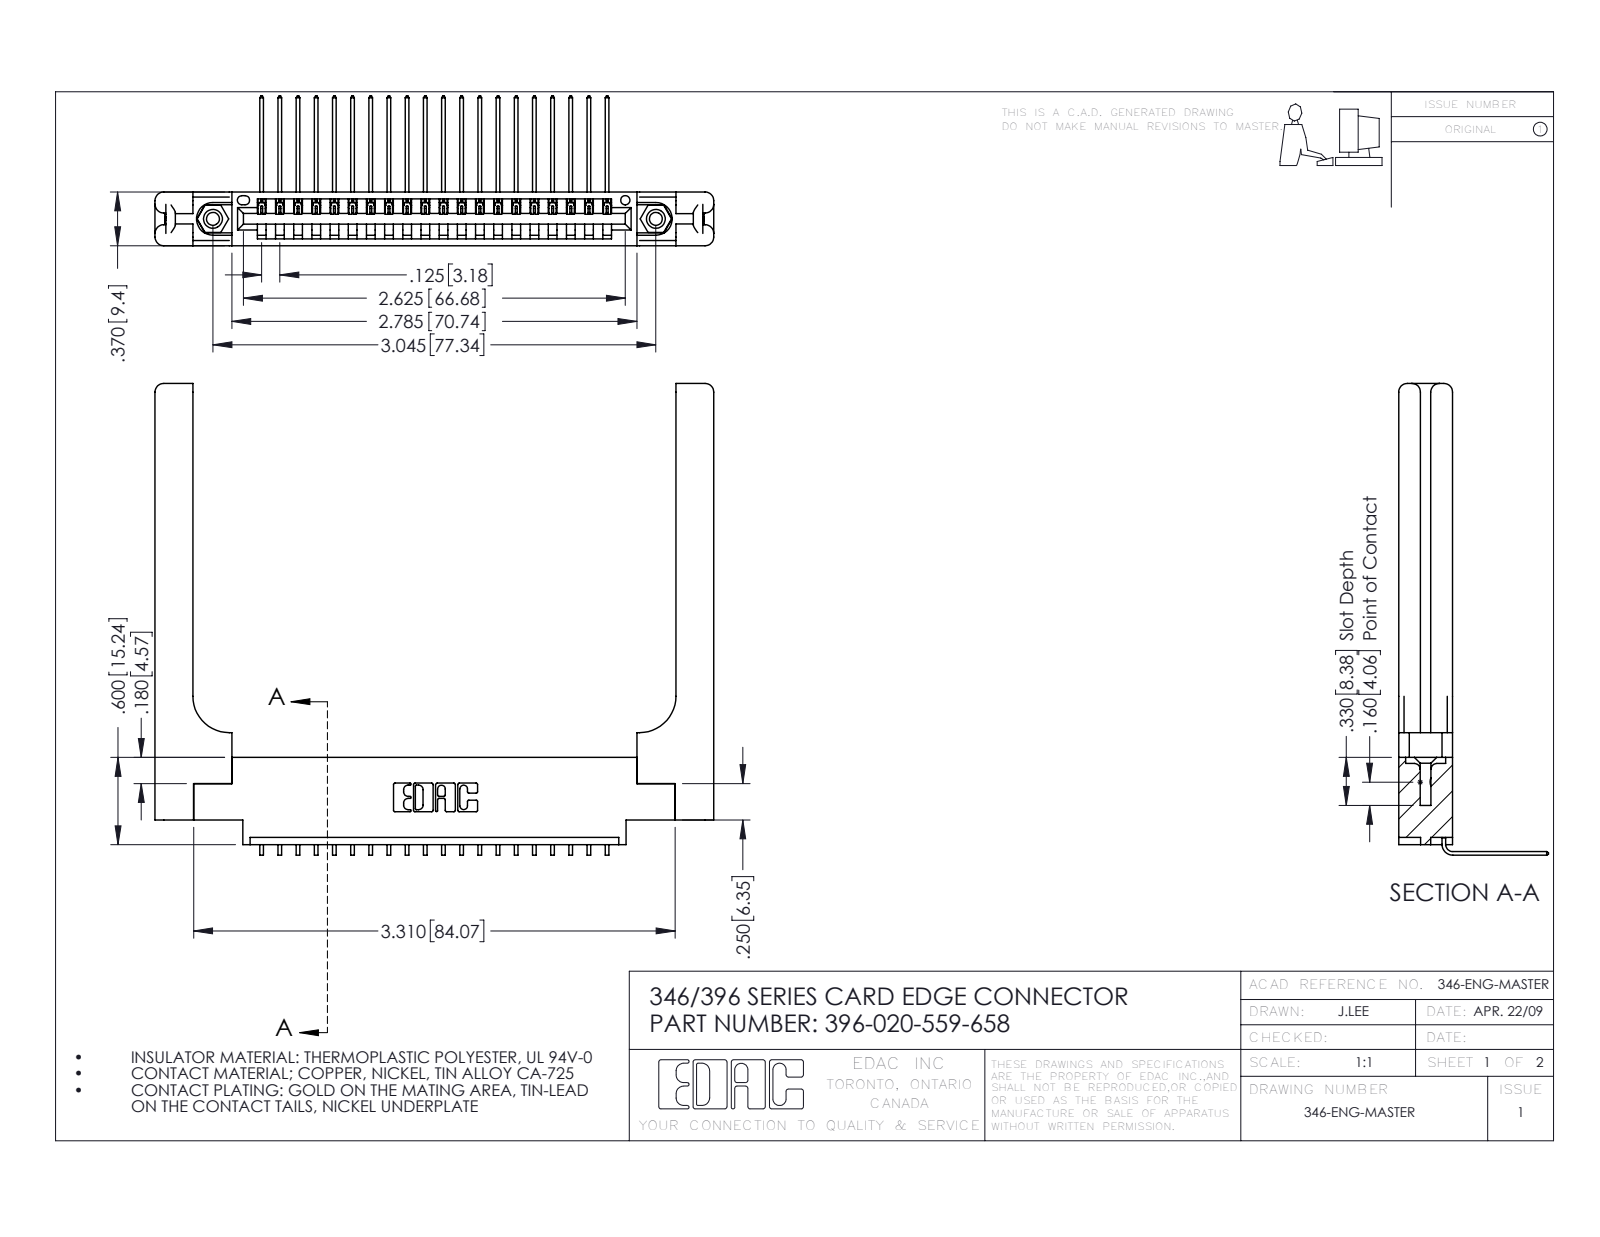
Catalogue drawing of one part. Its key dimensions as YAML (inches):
part_name: "346 Part_0.170 Offset - 0.156 Dia-TH; 396-020-559-658; 345-292-001_558 559 Tail - 1; 346-220-058_345-220-058 (+1 more)"
step_written_by: "SolidWorks 2016 (CONFIG_CONTROL_DESIGN)"
units: inches
bodies: {solids: 25, faces: 1582, planar: 1068, cylindrical: 454, other: 60}
overall_size: [3.841, 3.243, 1.03]
volume: 1.014
surface_area: 26.14
round_holes:
  - {diameter: 0.089, count: 2}
  - {diameter: 0.125, count: 2}
  - {diameter: 0.156, count: 2}
  - {diameter: 0.064, count: 1}
round_bosses_or_shafts:
  - {diameter: 0.155, count: 2}
partial_cylinders:
  - {radius: 0.006, count: 40}
  - {radius: 0.01, count: 22}
  - {radius: 0.06, count: 16}
  - {radius: 0.007, count: 6}
  - {radius: 0.031, count: 6}
  - {radius: 0.026, count: 3}
  - {radius: 0.03, count: 2}
  - {radius: 0.031, count: 2}
face_to_face_distances: [0.37, 0.072, 0.15, 0.048, 0.148, 0.322, 0.025, 0.25, 0.102, 0.22]
hole_center_spacings: [0.246, 2.837, 3.045]
